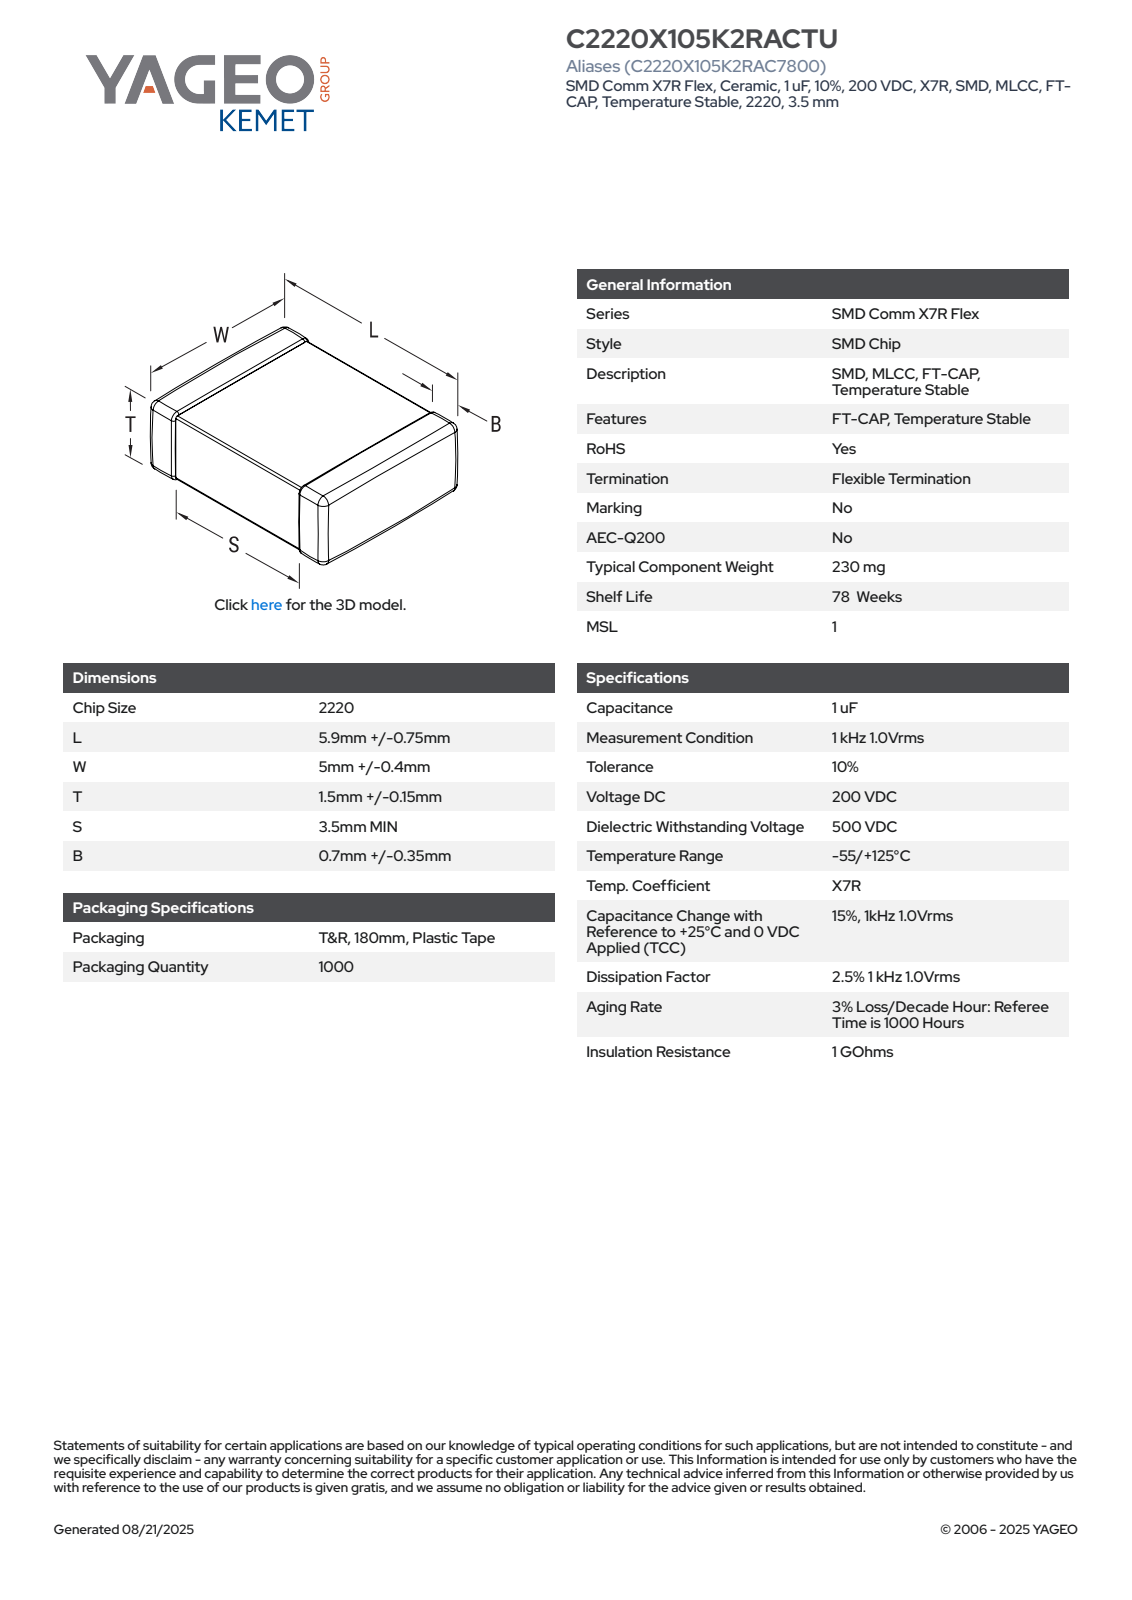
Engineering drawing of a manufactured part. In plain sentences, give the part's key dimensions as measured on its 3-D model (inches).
The part is named "CCS_CCSTDNOS_2220_L6.65W5.4T1.65B1.05". Its 3-D file was written by "SolidWorks 2014 (AUTOMOTIVE_DESIGN)". It is 4 solids with 121 faces: 71 planar, 34 cylindrical and 16 other. Overall it measures 0.262 by 0.213 by 0.065 inches. Its volume is 0.003 cubic inches and its surface area 0.167 square inches. Partial cylindrical surfaces (rounded edges, fillets, slot ends): 24 of radius 0.004. The main face-to-face distances are 0.056, 0.061, 0.065, 0.262, 0.204, 0.208, 0.213, 0.099, 0.109, 0.103.
